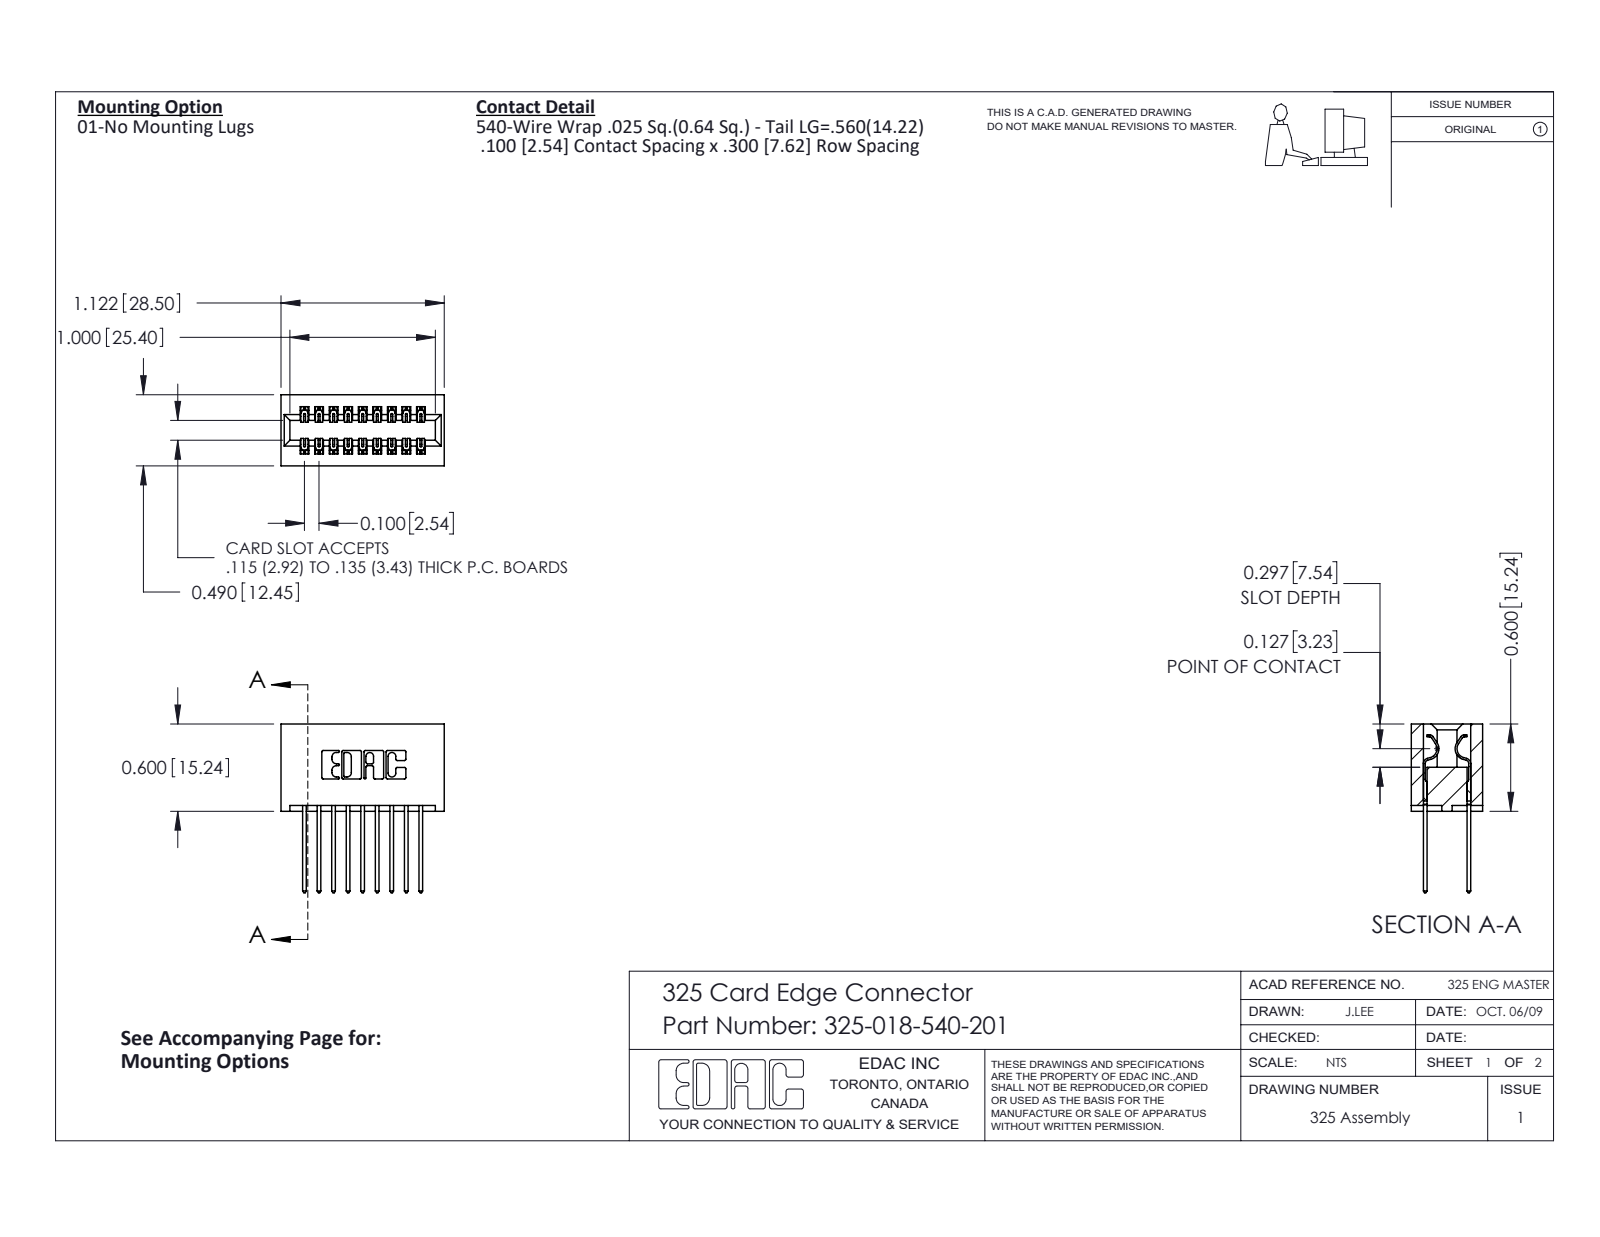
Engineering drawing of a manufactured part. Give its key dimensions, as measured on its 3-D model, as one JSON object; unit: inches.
{"part_name": "325-292-001_325-293-140; 325 Part_Lugless; 325-018-540-201", "step_written_by": "SolidWorks 2016 (CONFIG_CONTROL_DESIGN)", "units": "inches", "bodies": {"solids": 19, "faces": 1042, "planar": 714, "cylindrical": 328, "other": 0}, "overall_size": [1.16, 1.122, 0.49], "volume_in3": 0.248, "surface_area_in2": 7.927, "partial_cylinders_radius": [[0.006, 27], [0.01, 22], [0.01, 18], [0.007, 6], [0.031, 6], [0.026, 3], [0.014, 2], [0.022, 2]], "face_to_face_distances": [0.3, 0.083, 0.407, 0.1, 0.2, 0.107, 0.383, 0.025, 0.4, 0.04]}
